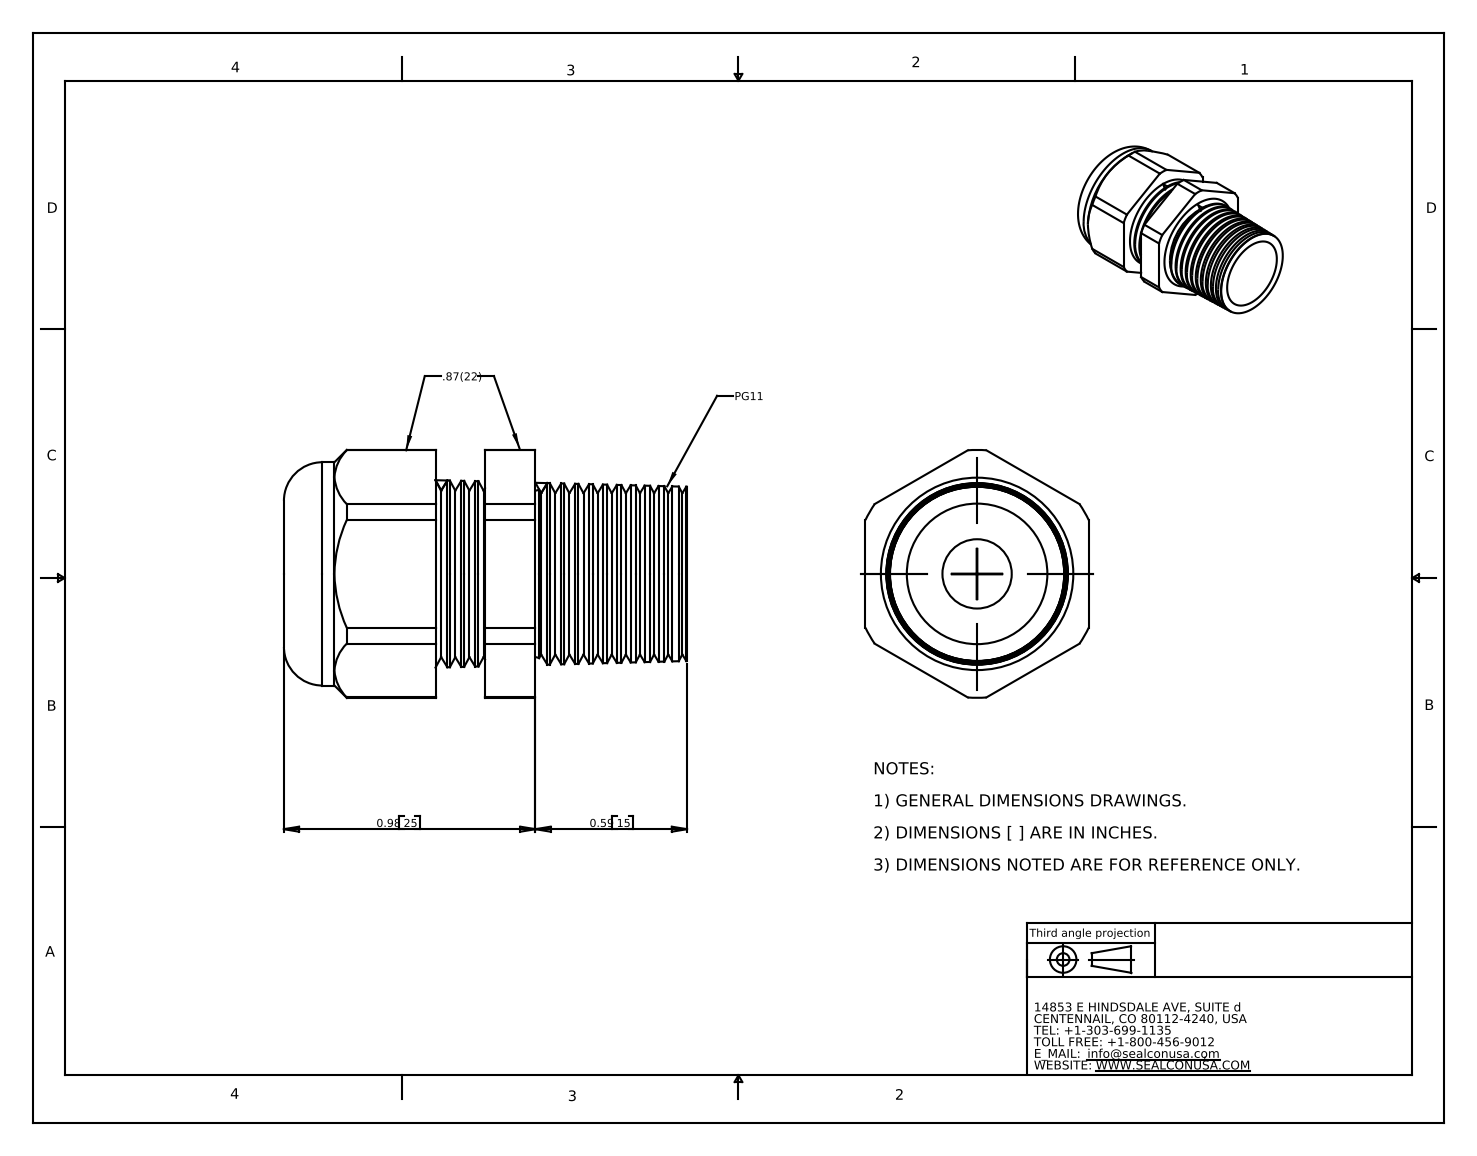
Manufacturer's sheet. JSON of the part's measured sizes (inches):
{"part_name": "CD11CR-GY", "step_written_by": "SolidWorks 2007 (CONFIG_CONTROL_DESIGN)", "units": "inches", "bodies": {"solids": 2, "faces": 148, "planar": 20, "cylindrical": 22, "other": 106}, "overall_size": [1.57, 0.966, 0.87], "volume_in3": 0.594, "surface_area_in2": 9.303, "round_holes": [[0.27, 1], [0.547, 1]], "round_bosses_or_shafts": [[0.87, 1]], "partial_cylinders_radius": [[0.483, 1]], "face_to_face_distances": [0.87, 0.587, 0.394, 0.193, 0.197, 0.783, 0.39, 0.167, 0.56, 0.753]}
